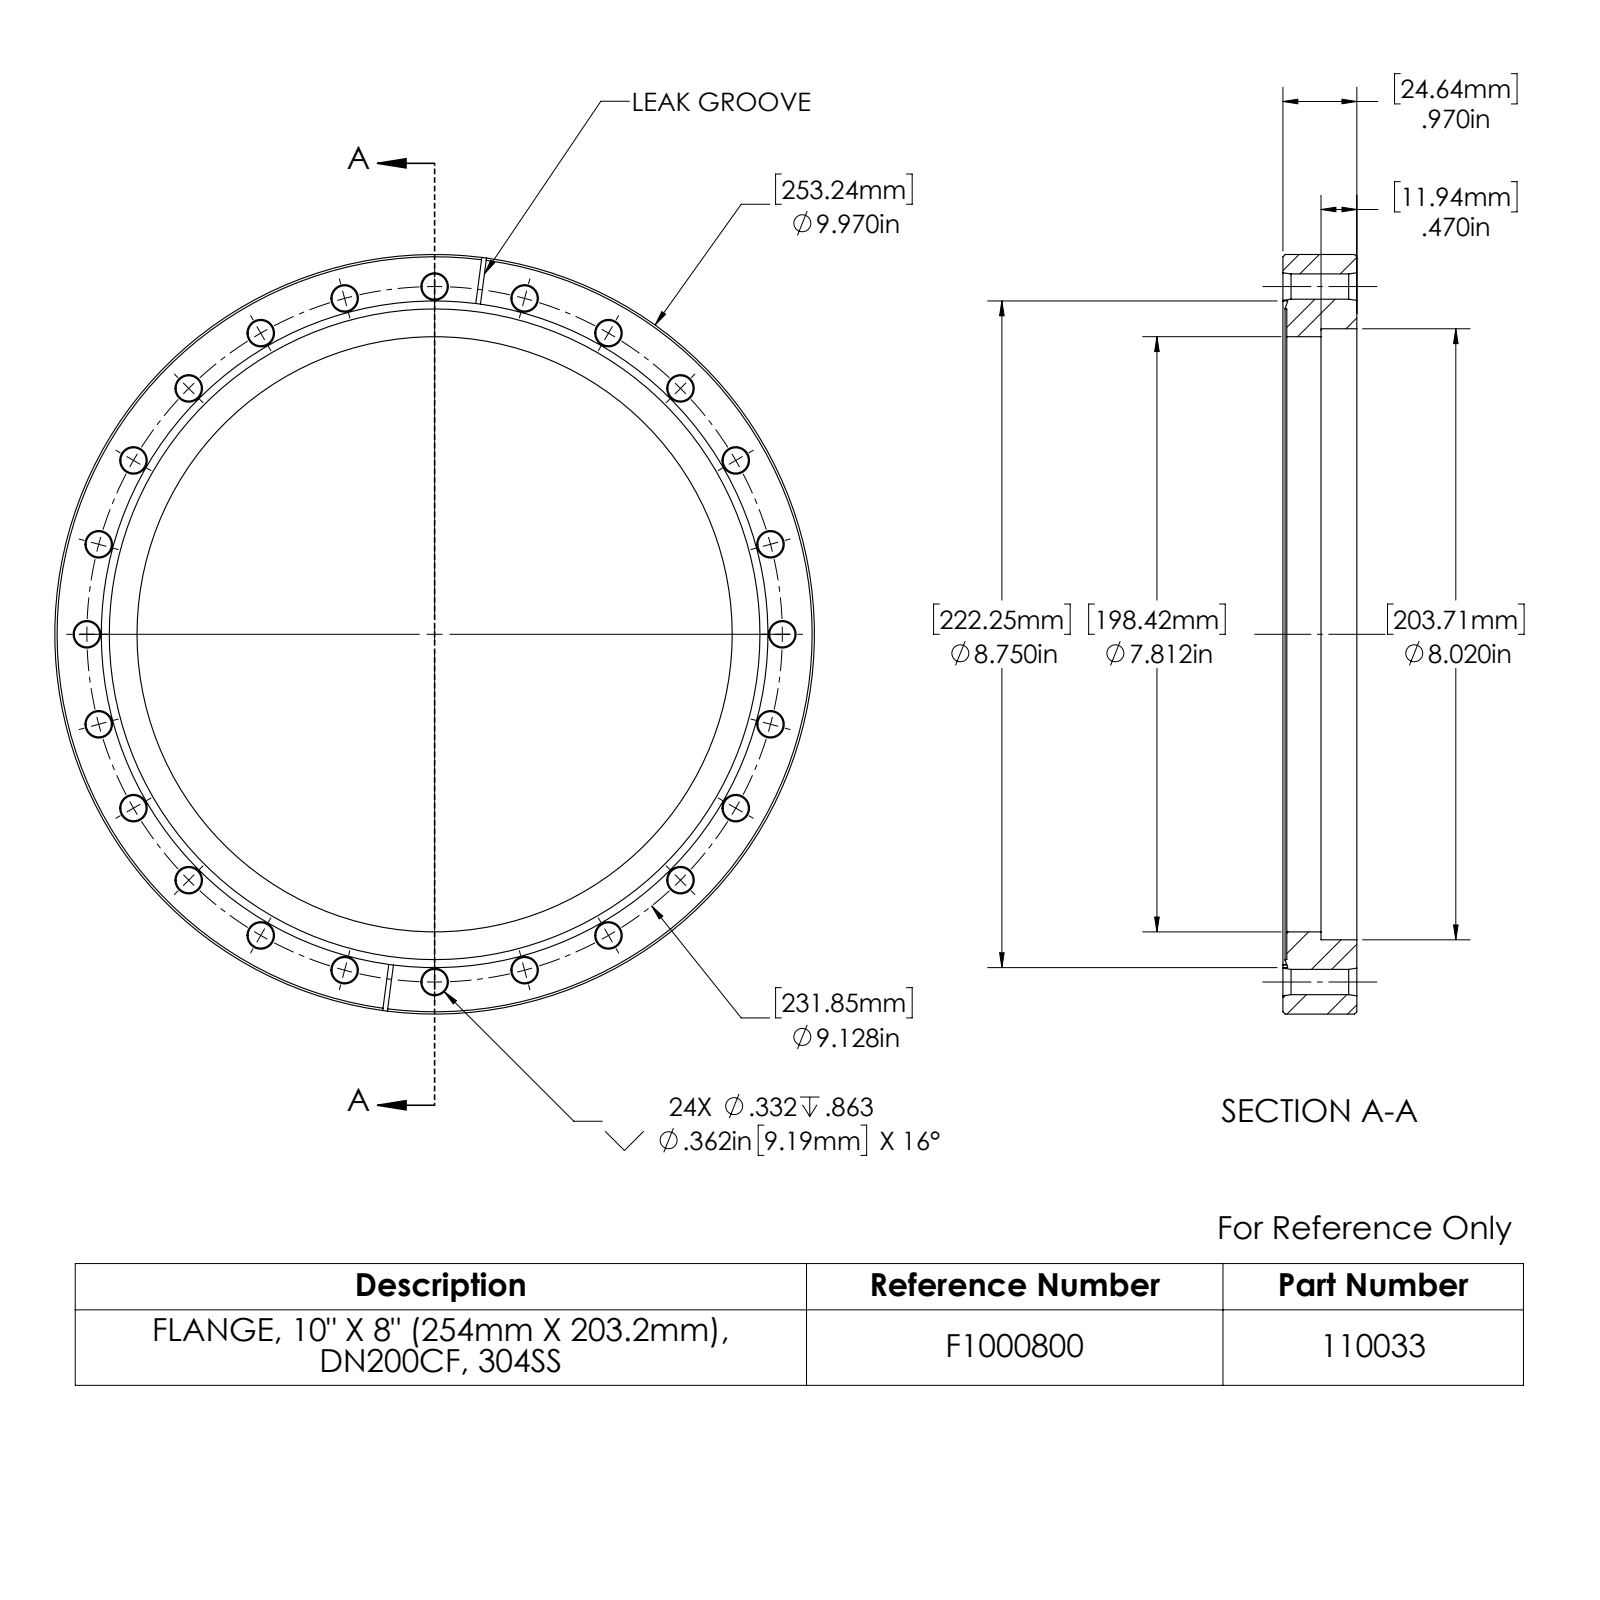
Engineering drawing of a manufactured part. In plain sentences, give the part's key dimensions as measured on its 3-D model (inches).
The part is named "110033". Its 3-D file was written by "SolidWorks 2022 (AUTOMOTIVE_DESIGN)". It is 1 solid with 180 faces: 9 planar, 60 cylindrical and 111 other. Overall it measures 9.97 by 9.97 by 0.97 inches. Its volume is 25.32 cubic inches and its surface area 134.6 square inches. Round holes: 24 of diameter 0.332, 1 of diameter 7.812, 1 of diameter 8.02, 1 of diameter 8.54, 1 of diameter 8.75. Round bosses or shafts: 1 of diameter 9.97. Partial cylindrical surfaces (rounded edges, fillets, slot ends): 2 of radius 1.25. The main face-to-face distances are 0.97, 0.051, 0.919, 0.5, 0.449, 0.47, 0.062. The hole center spacings are 4.564, 8.433, 2.363, 4.564, 7.905, 1.191, 3.493, 5.557.
